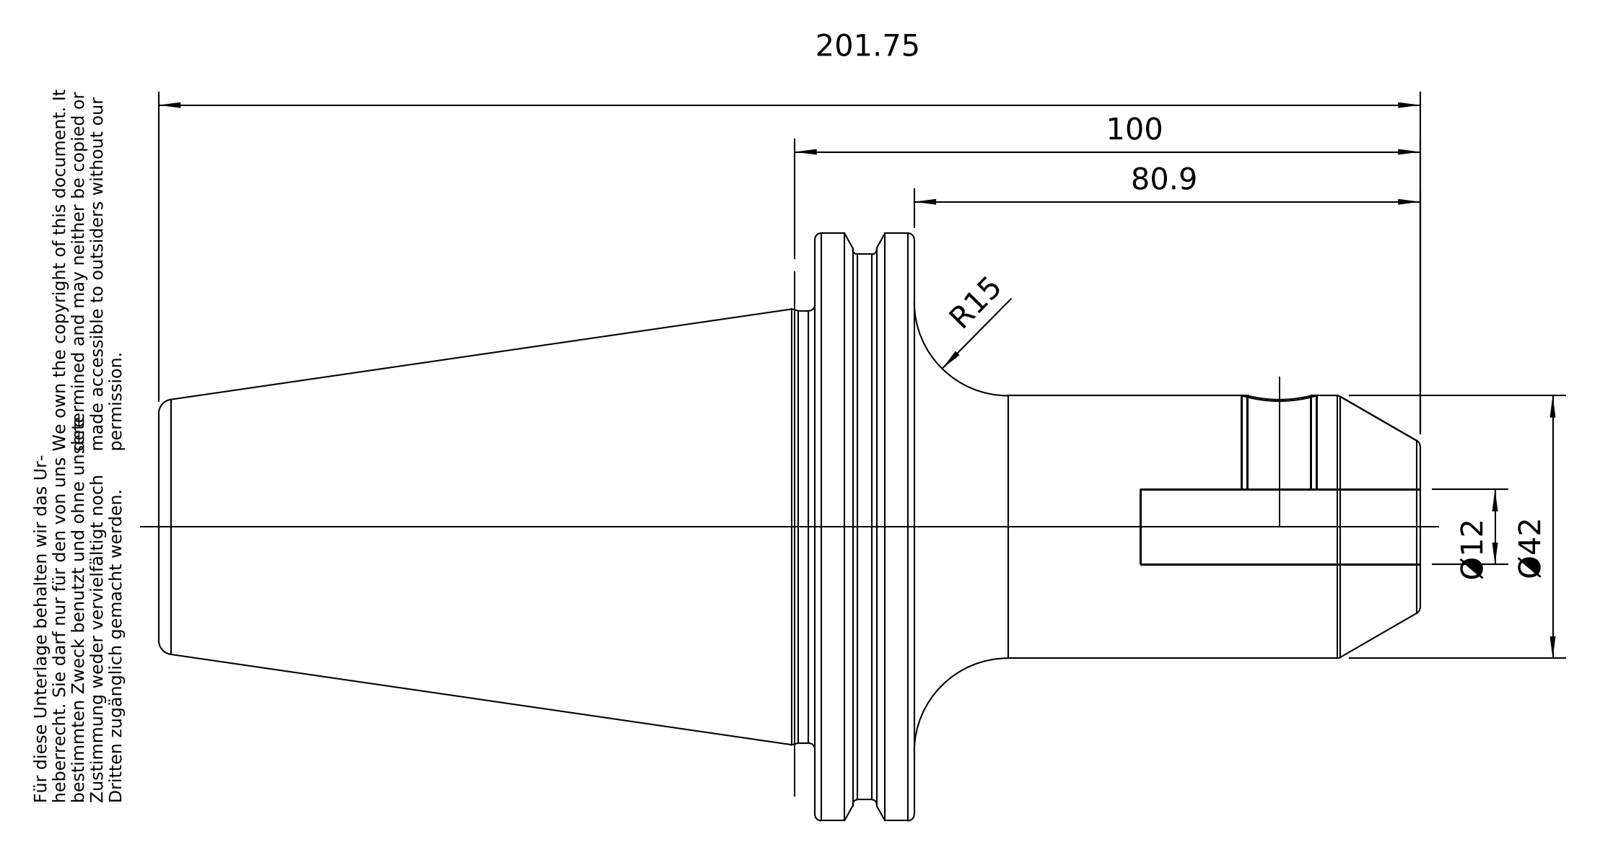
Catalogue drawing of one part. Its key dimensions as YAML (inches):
part_name: "50-301-12"
step_written_by: "PRO/ENGINEER BY PARAMETRIC TECHNOLOGY CORPORATION, 2010430 (CONFIG_CONTROL_DESIGN)"
units: inches
bodies: {solids: 1, faces: 103, planar: 21, cylindrical: 32, other: 50}
overall_size: [7.937, 3.837, 3.701]
volume: 27.28
surface_area: 84.07
round_holes:
  - {diameter: 0.472, count: 2}
  - {diameter: 0.402, count: 1}
  - {diameter: 0.817, count: 1}
  - {diameter: 0.985, count: 1}
  - {diameter: 1.012, count: 1}
round_bosses_or_shafts:
  - {diameter: 3.583, count: 1}
  - {diameter: 2.722, count: 1}
  - {diameter: 1.654, count: 1}
  - {diameter: 0.945, count: 1}
partial_cylinders:
  - {radius: 0.069, count: 5}
  - {radius: 1.919, count: 1}
face_to_face_distances: [0.624, 3.811, 3.187, 4.126, 4.75, 7.937, 2.866, 1.016, 1.89, 2.236]
